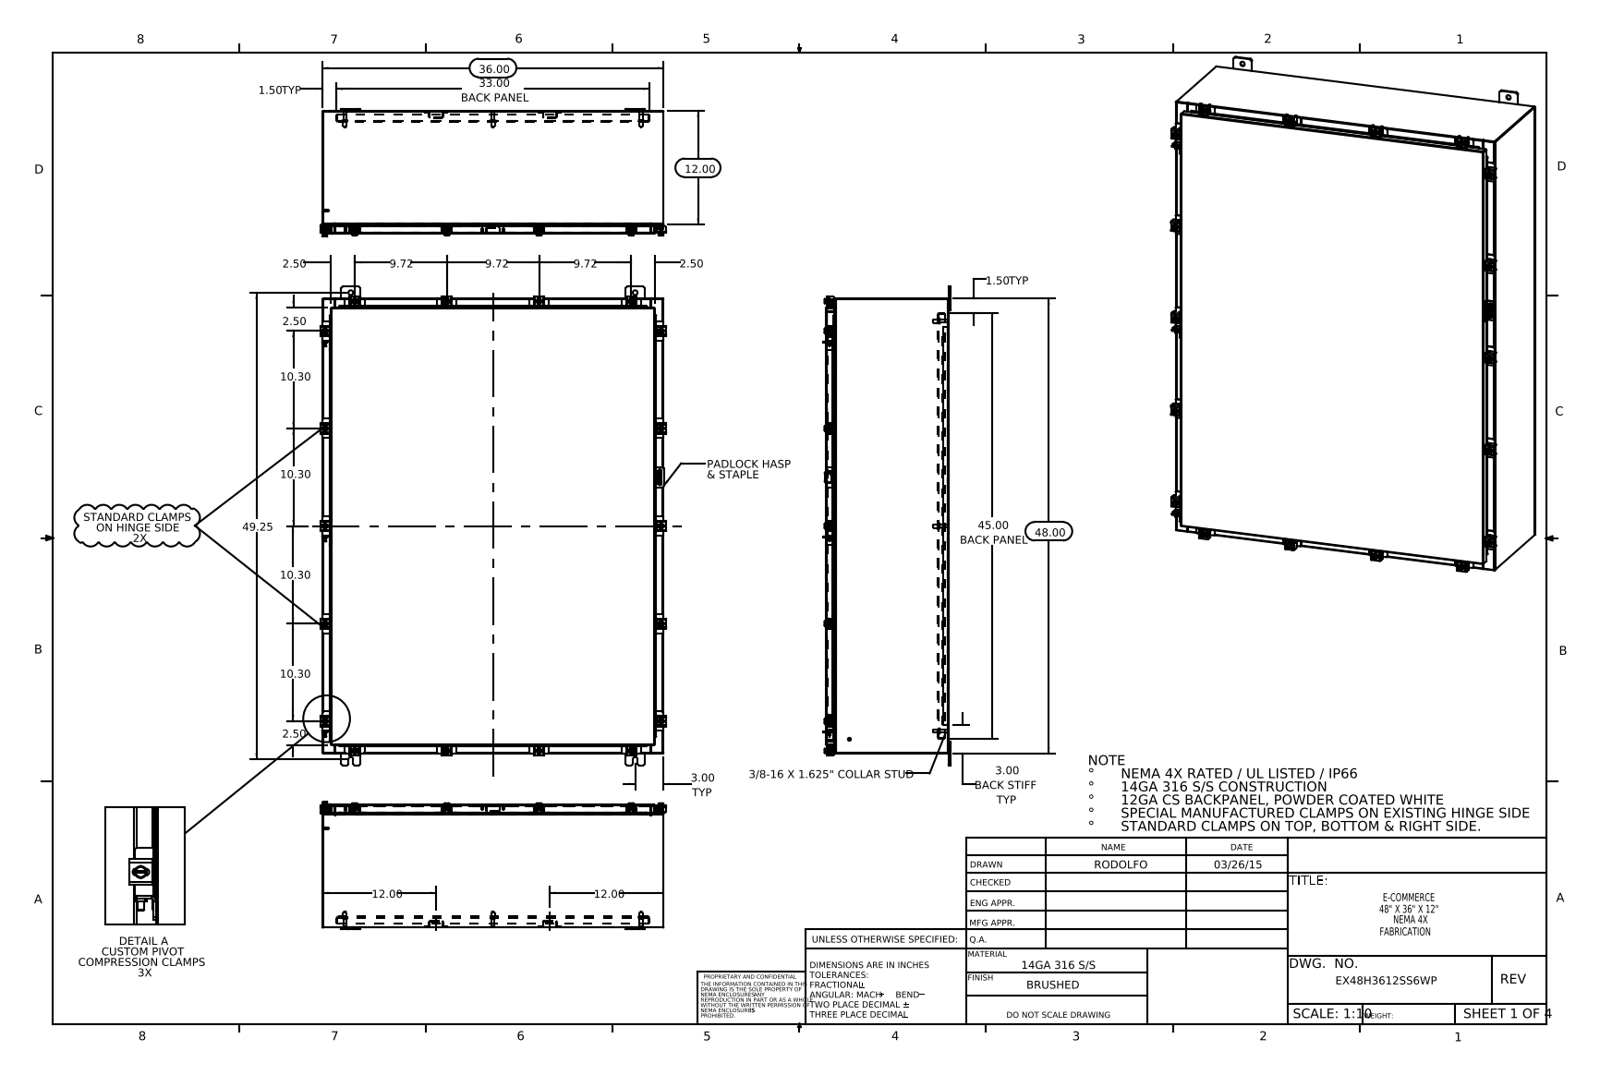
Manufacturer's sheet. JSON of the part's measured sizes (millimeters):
{"part_name": "EX48H3612SS6WP Special Clamp; ATEX CLAMP HINGE BRAKET; EX48H3612SS6WP Padlock Hasp; Special Clamp Assembly (+8 more)", "step_written_by": "SolidWorks 2014 (CONFIG_CONTROL_DESIGN)", "units": "millimeters", "bodies": {"solids": 126, "faces": 3106, "planar": 1613, "cylindrical": 1195, "other": 298}, "overall_size": [1282.7, 925.1, 341.7], "volume_mm3": 10630000, "surface_area_mm2": 10410000, "round_holes": [[5.4, 18], [6.6, 18], [12.7, 12], [6.4, 7], [3.2, 1]], "round_bosses_or_shafts": [[12.7, 18], [6.4, 18], [10.1, 15], [15.9, 8], [9.5, 8], [8.4, 8], [4, 6], [3.6, 6]], "partial_cylinders_radius": [[1.5, 76], [0.3, 38], [3.6, 36], [2.2, 34], [3, 33], [2.3, 27], [1.3, 25], [3.7, 24]], "face_to_face_distances": [1.9, 327.7, 325.8, 329.6, 2.6, 25.4, 27.3, 300.4, 302.3, 29.9], "hole_center_spacings": [50, 59.6, 112.8, 354.9, 374.1, 409.6, 422.2, 451]}
